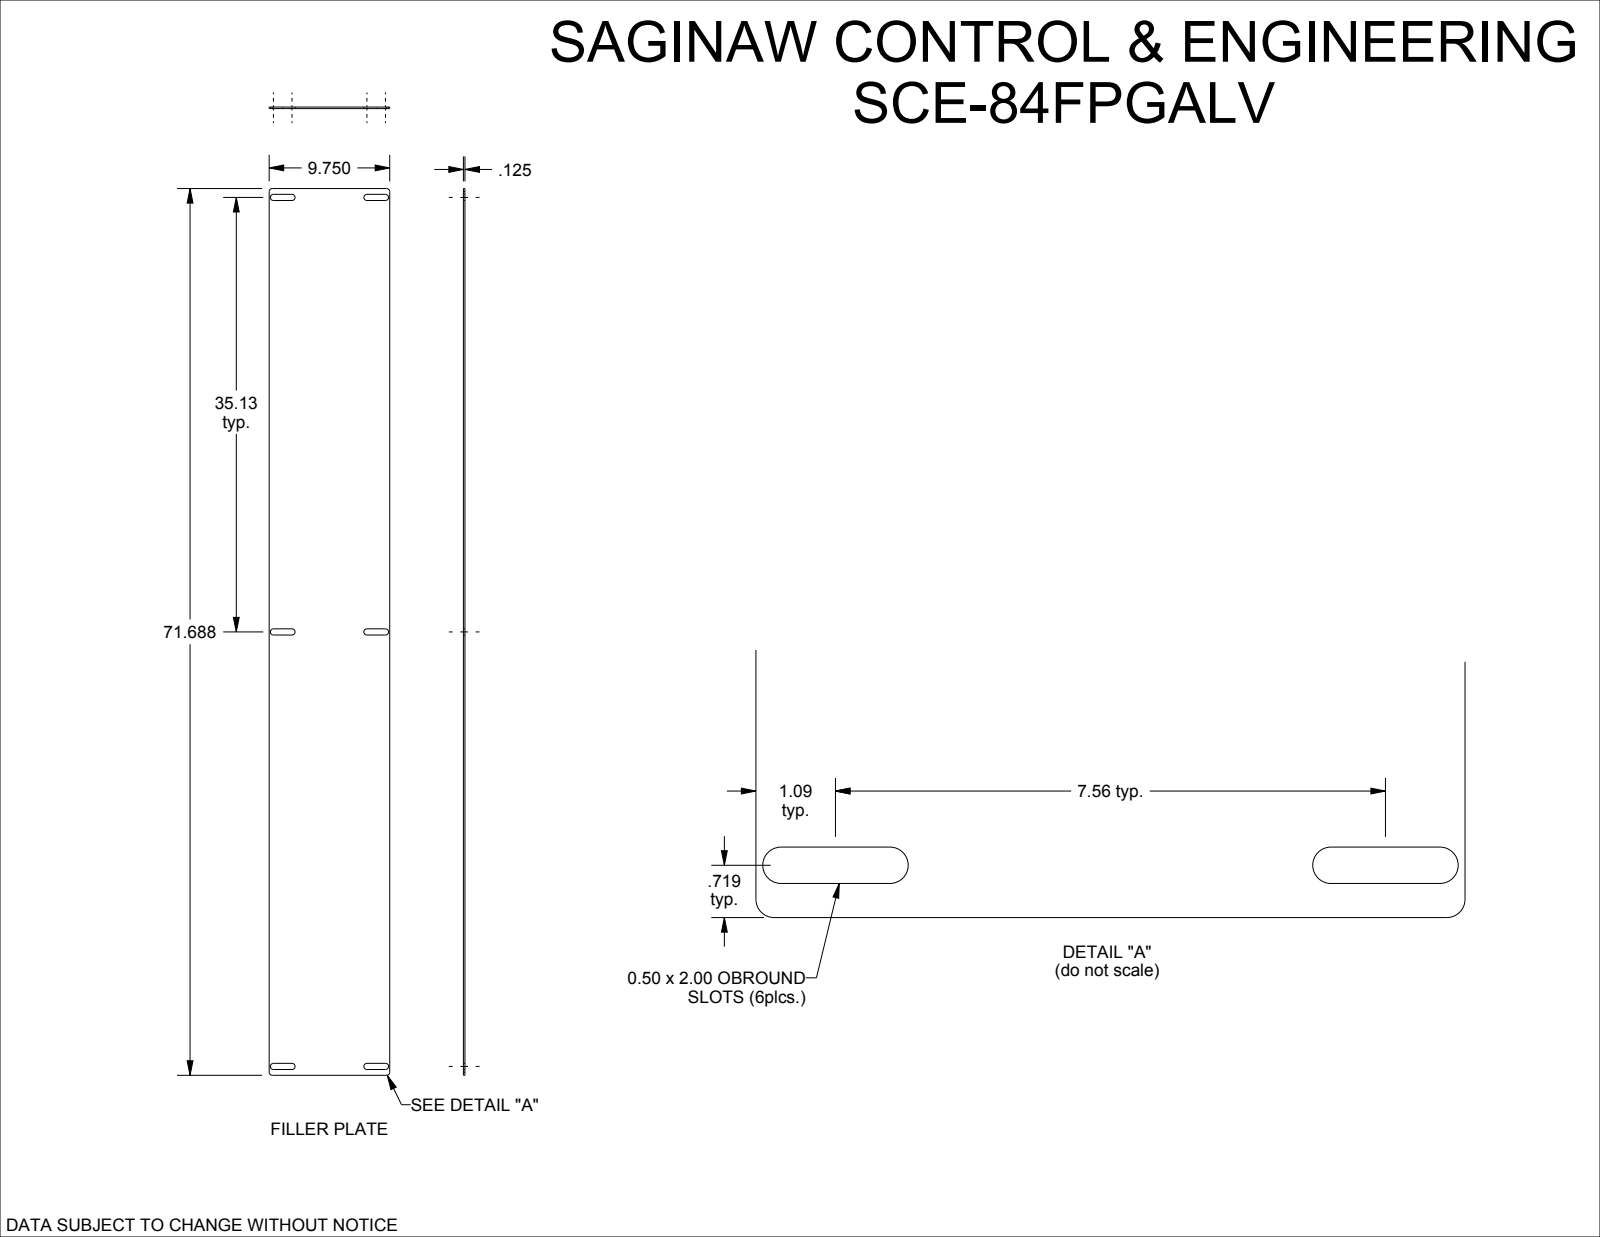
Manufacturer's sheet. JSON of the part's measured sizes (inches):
{"part_name": "SCE-84FPGALV", "step_written_by": "SolidWorks 2023 (AUTOMOTIVE_DESIGN)", "units": "inches", "bodies": {"solids": 1, "faces": 46, "planar": 30, "cylindrical": 16, "other": 0}, "overall_size": [71.687, 9.75, 0.125], "volume_in3": 86.65, "surface_area_in2": 1410, "partial_cylinders_radius": [[0.25, 16]], "face_to_face_distances": [0.125, 9.75, 35.125, 71.687, 0.5, 35.594, 36.094, 0.469, 71.219, 0.969]}
